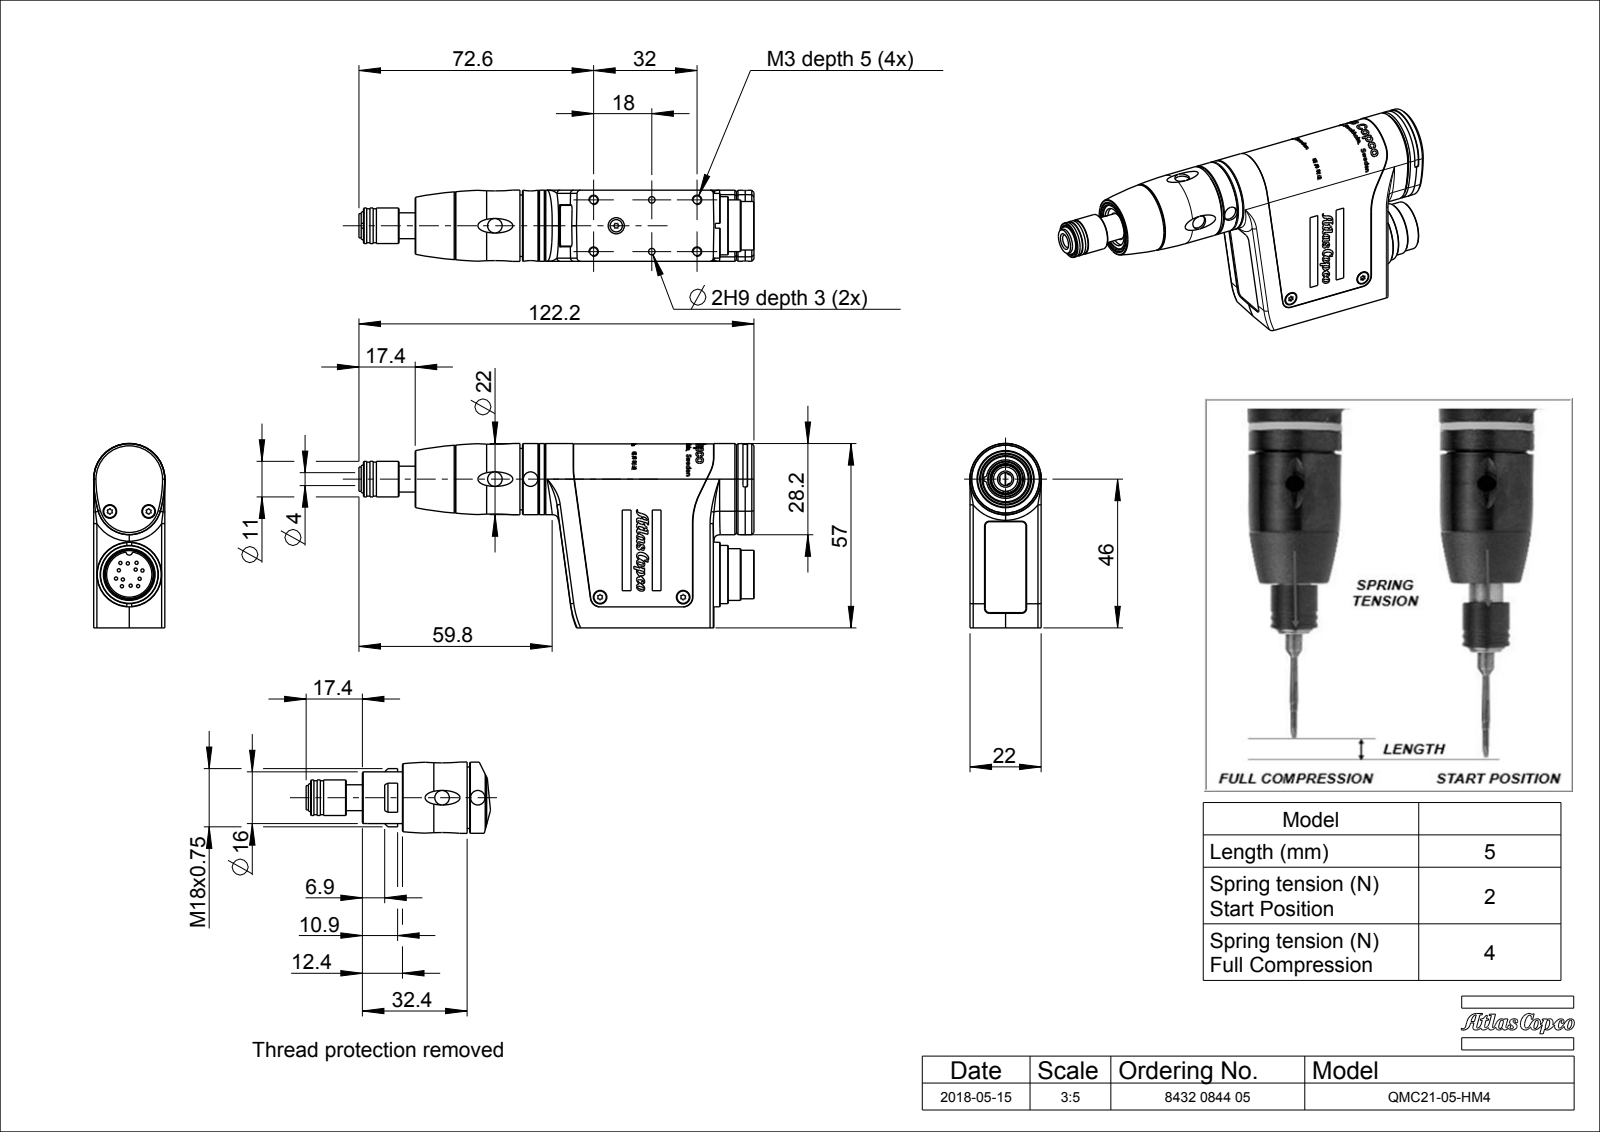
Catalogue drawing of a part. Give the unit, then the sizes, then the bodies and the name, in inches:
Units: inches
Overall size (bounding box): 4.812 × 2.245 × 0.869
Round holes (diameter × count): ⌀0.079 ×7, ⌀0.063 ×4, ⌀0.098 ×4, ⌀0.118 ×4, ⌀0.067 ×3, ⌀0.083 ×3, ⌀0.087 ×3, ⌀0.177 ×3, ⌀0.039 ×2, ⌀0.047 ×2, ⌀0.551 ×2, ⌀0.043 ×1
Round bosses / shafts (diameter × count): ⌀0.039 ×12, ⌀0.028 ×12, ⌀0.024 ×12, ⌀0.15 ×5, ⌀0.709 ×2, ⌀0.591 ×2, ⌀0.866 ×1, ⌀0.787 ×1
Partial cylindrical surfaces — rounded edges, fillets, slot ends (radius × count): R0.02 ×19, R0.004 ×18, R0.118 ×16, R0.039 ×13, R0.007 ×12, R0.013 ×12, R0.021 ×12, R0.079 ×8
Main face-to-face distances: 0.839, 0.02, 0.819, 0.858, 0.024, 0.843, 0.862, 0.866, 0.079, 0.039
Hole centre spacings: 0.63, 0.388, 0.419, 0.459, 0.535, 0.551, 0.709, 0.726
Volume: 1.664 in³ · Surface area: 58.14 in²
Bodies: 21 solids, 1371 faces (379 planar, 640 cylindrical, 352 other)
Part name (STEP PRODUCT): 4216245104; 0993000295_SPEC_3; 4216240420_AF0_ASM; 4216240480_ASM (+8 more)
STEP written by: CREO PARAMETRIC BY PTC INC, 2016260 (CONFIG_CONTROL_DESIGN)
